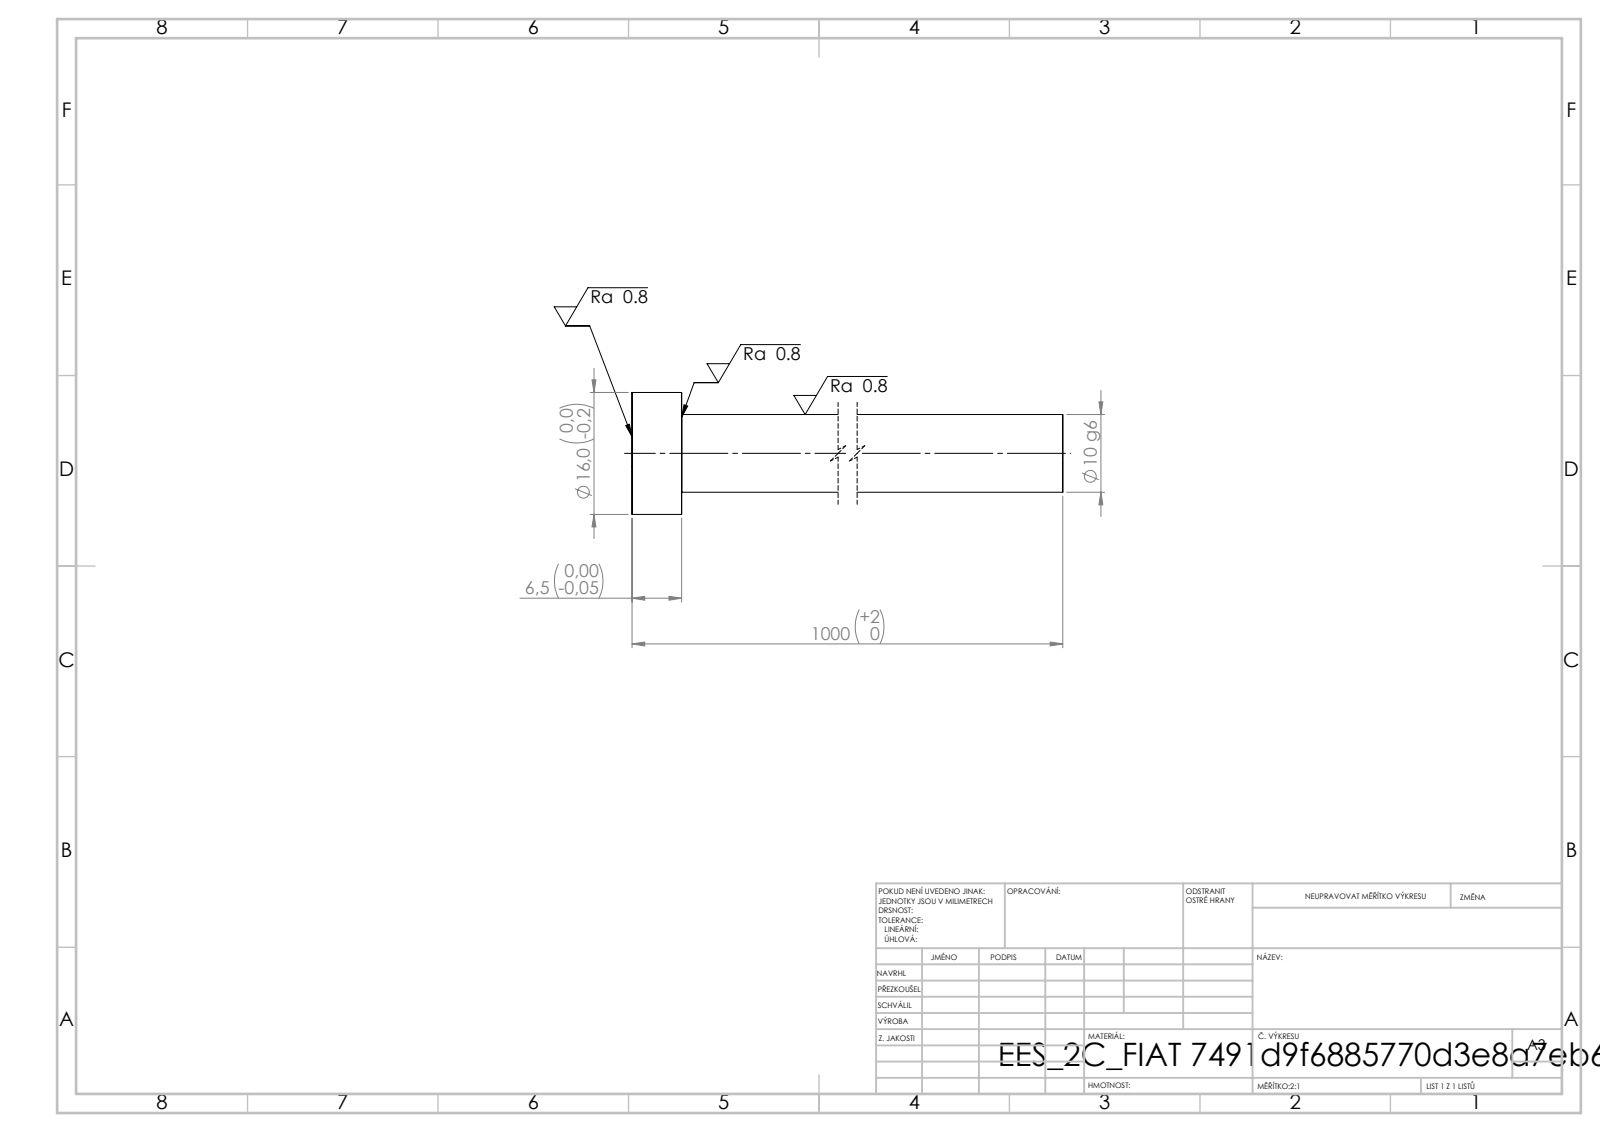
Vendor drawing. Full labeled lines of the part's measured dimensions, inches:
STEP written by: SolidWorks 2019 (CONFIG_CONTROL_DESIGN)
Units: inches
Bodies: 1 solid, 7 faces (3 planar, 4 cylindrical, 0 other)
Overall size (bounding box): 39.37 × 0.63 × 0.63
Volume: 5.034 in³ · Surface area: 50.48 in²
Round bosses / shafts (diameter × count): ⌀0.63 ×1, ⌀0.402 ×1
Main face-to-face distances: 0.256, 39.37, 39.114
